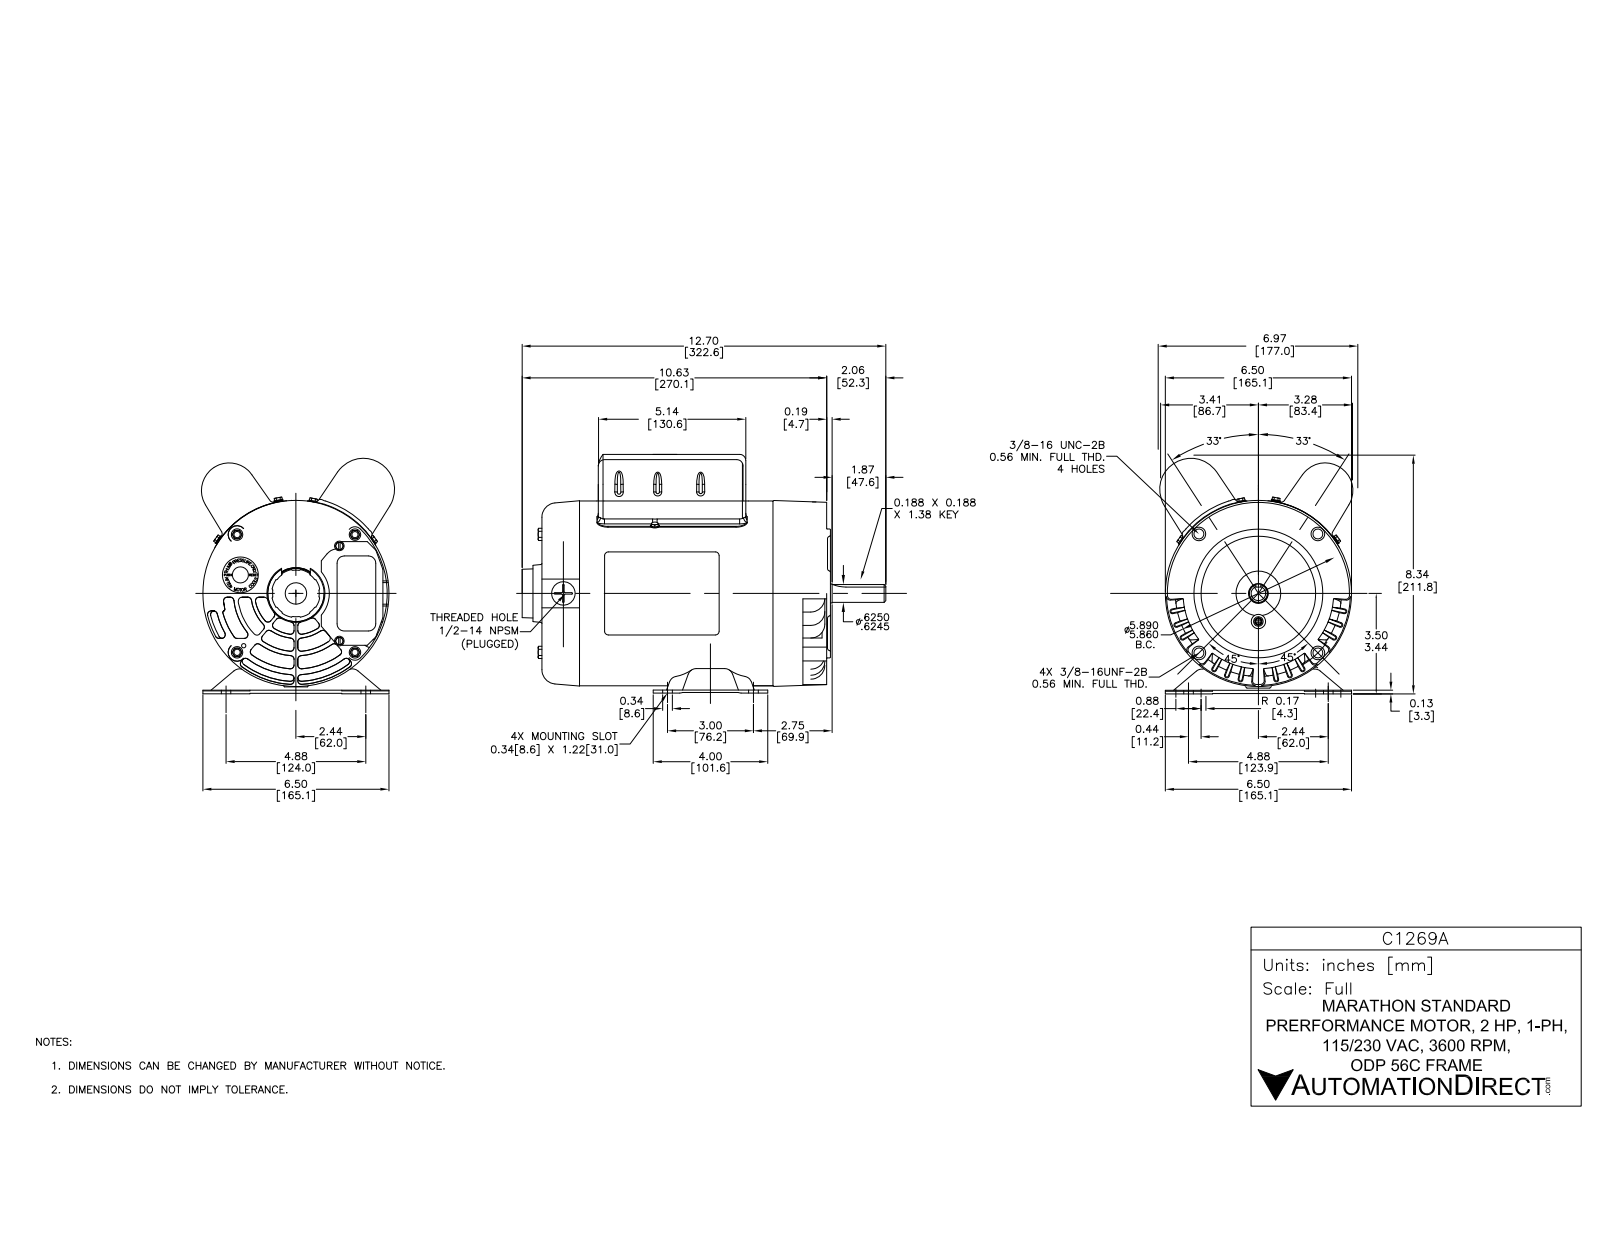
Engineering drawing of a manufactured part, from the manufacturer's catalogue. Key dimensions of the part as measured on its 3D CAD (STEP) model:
Part name (STEP PRODUCT): SS84236-725_Rev13
STEP written by: SolidWorks 2015 (CONFIG_CONTROL_DESIGN)
Units: inches
Bodies: 36 solids, 3834 faces (1080 planar, 919 cylindrical, 1835 other)
Overall size (bounding box): 18.443 × 15.474 × 13.178
Volume: 349.7 in³ · Surface area: 2 337 in²
Round holes (diameter × count): ⌀0.05 ×11, ⌀0.15 ×10, ⌀0.12 ×9, ⌀0.257 ×9, ⌀0.25 ×8, ⌀0.187 ×7, ⌀0.201 ×6, ⌀0.087 ×4, ⌀0.31 ×4, ⌀0.332 ×4, ⌀0.344 ×4, ⌀0.437 ×4
Round bosses / shafts (diameter × count): ⌀0.5 ×8, ⌀0.11 ×7, ⌀0.313 ×4, ⌀0.31 ×4, ⌀9.811 ×1, ⌀7.38 ×1, ⌀3 ×1, ⌀2.37 ×1
Partial cylindrical surfaces — rounded edges, fillets, slot ends (radius × count): R0.12 ×76, R0.02 ×72, R0.25 ×59, R0.08 ×48, R0.2 ×48, R0.1 ×47, R0.05 ×16, R0.36 ×12
Main face-to-face distances: 0.12, 0.31, 0.19, 0.12, 14.54, 2.32, 9.57, 2.936, 2.817, 2.65
Hole centre spacings: 0.964, 1.642, 2.386, 3.841, 5.72, 6.126, 8.01, 3.25
